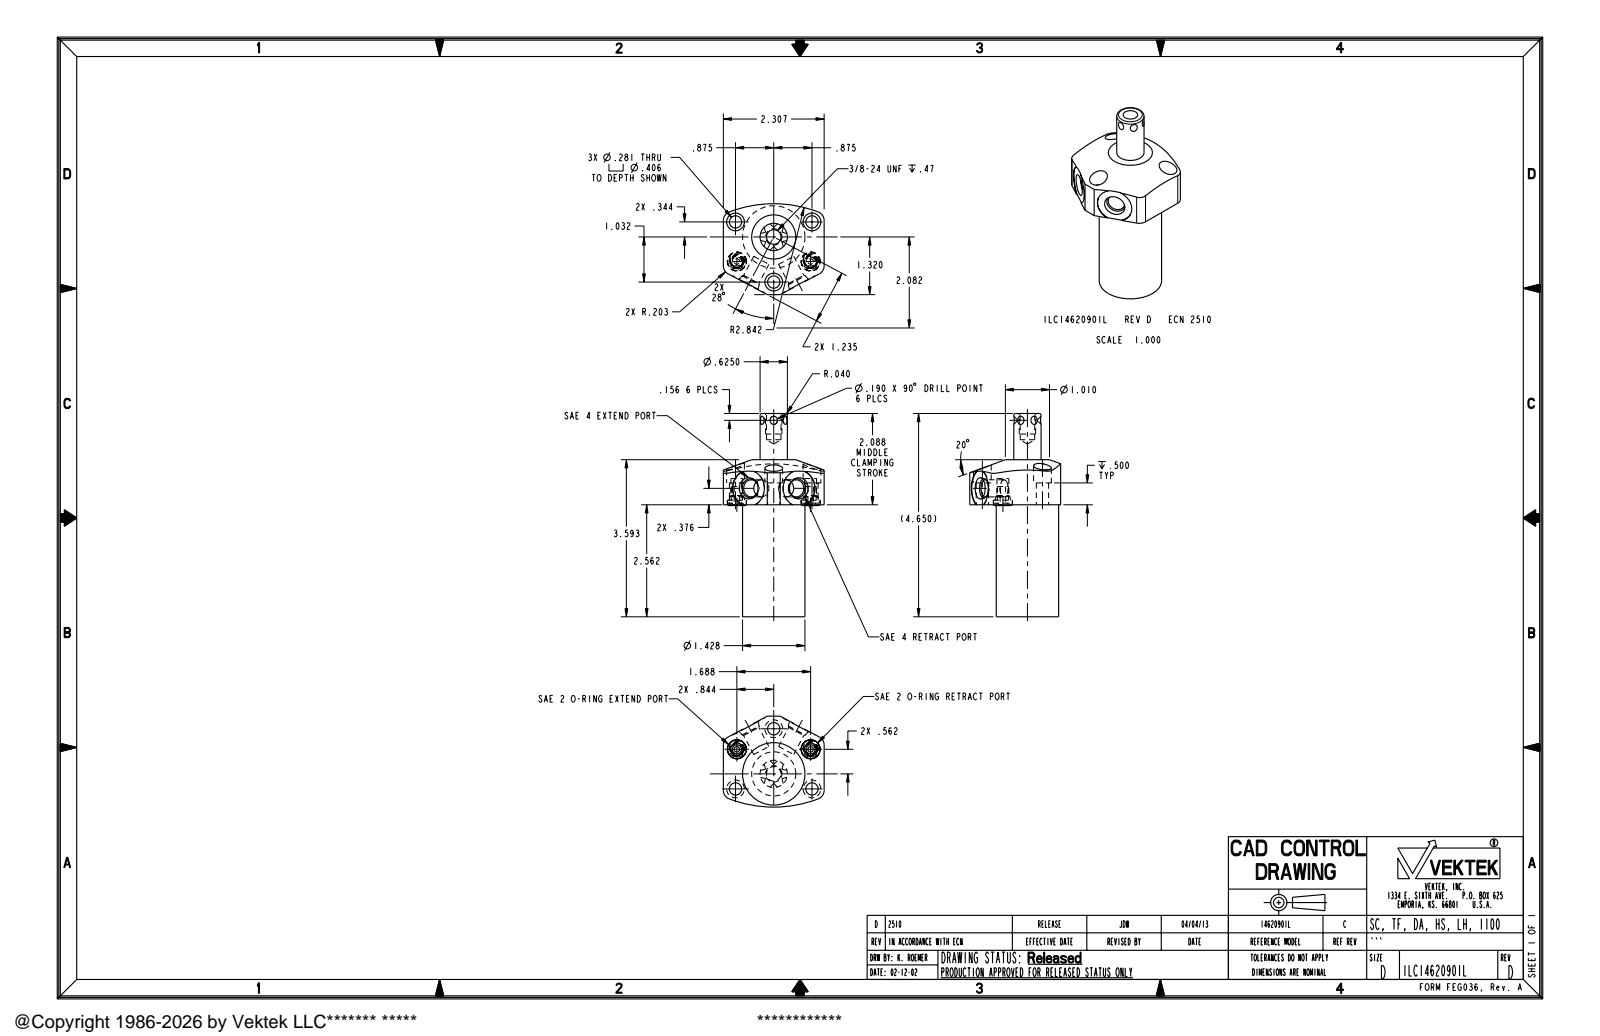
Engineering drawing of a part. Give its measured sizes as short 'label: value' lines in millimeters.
name: ILC14620901L
written by: PRO/ENGINEER BY PARAMETRIC TECHNOLOGY CORPORATION, 2007460 (AUTOMOTIVE_DESIGN_CC2)
unit: mm
bodies: 1 solid, 132 faces (33 planar, 57 cylindrical, 42 other)
size: 118.1 × 58.6 × 52.8
volume: 125 300 mm³; area: 22 970 mm²
holes: 3× ⌀7.1, 3× ⌀10.3, 2× ⌀3.2, 2× ⌀6.9, 2× ⌀10, 2× ⌀11.1, 1× ⌀8.4
bosses: 2× ⌀10.9, 2× ⌀6.5, 2× ⌀5.3, 1× ⌀36.3, 1× ⌀15.9, 1× ⌀9.5
rounds: 4× R5.2, 2× R10.5, 1× R72.2
face distances: 65.1, 58.6, 91.3, 26.2, 15.7, 77.8, 12.7, 13.5, 2.5, 12.6
hole spacings: 23, 23.9, 24.5, 25.8, 41.4, 49.4, 26.2, 42.9
